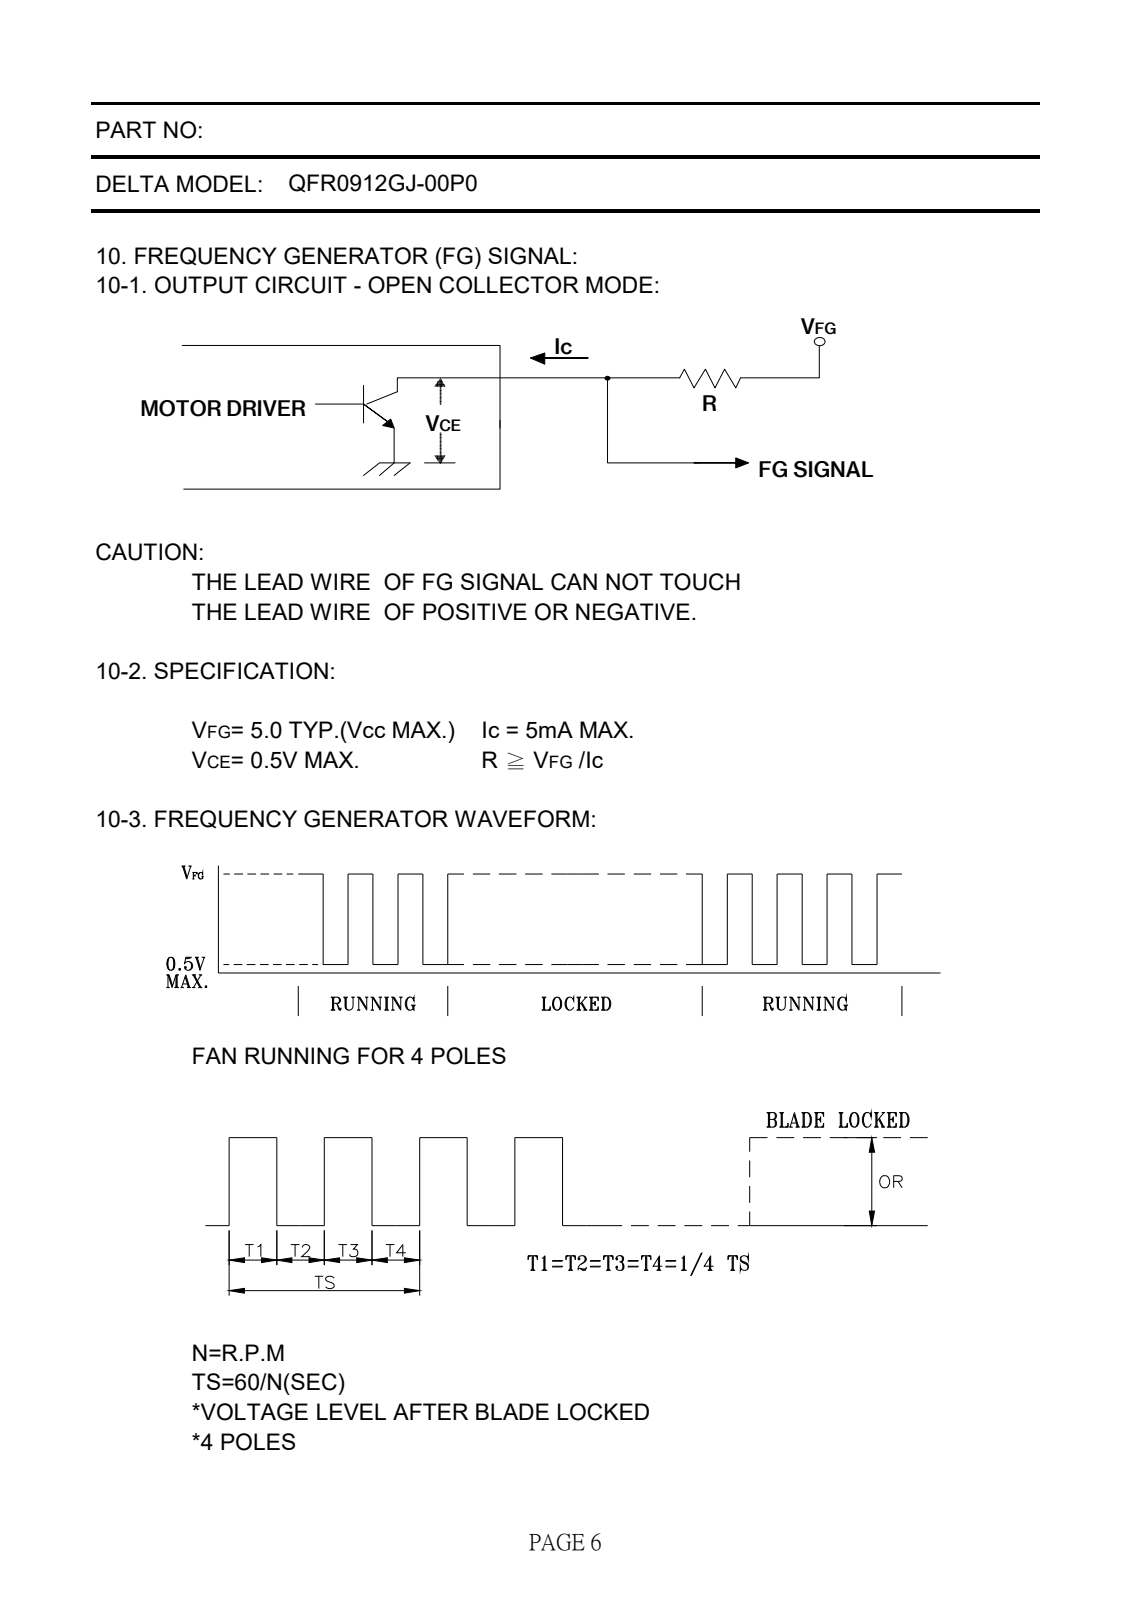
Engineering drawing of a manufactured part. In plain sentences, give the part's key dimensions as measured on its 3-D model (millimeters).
The part is named "QFR0912GJ-00P0_3D". Its 3-D file was written by "SolidWorks 2016 (CONFIG_CONTROL_DESIGN)". It is 1 solid with 820 faces: 471 planar, 208 cylindrical and 141 other. Overall it measures 92.4 by 92 by 25.5 millimeters. Its volume is 154 454 cubic millimeters and its surface area 37 200 square millimeters. Round holes: 4 of diameter 4.5, 1 of diameter 1.52, 1 of diameter 29.5. Round bosses or shafts: 1 of diameter 86.2. Partial cylindrical surfaces (rounded edges, fillets, slot ends): 58 of radius 0.5, 4 of radius 0.47, 4 of radius 1, 4 of radius 1.29, 4 of radius 1.68, 4 of radius 2.21, 4 of radius 2.59, 4 of radius 3. The main face-to-face distances are 21, 92, 21.4, 4, 1.3, 22.3, 2, 2.7, 18.3, 1.5. The hole center spacings are 58.34, 82.5, 116.67.
